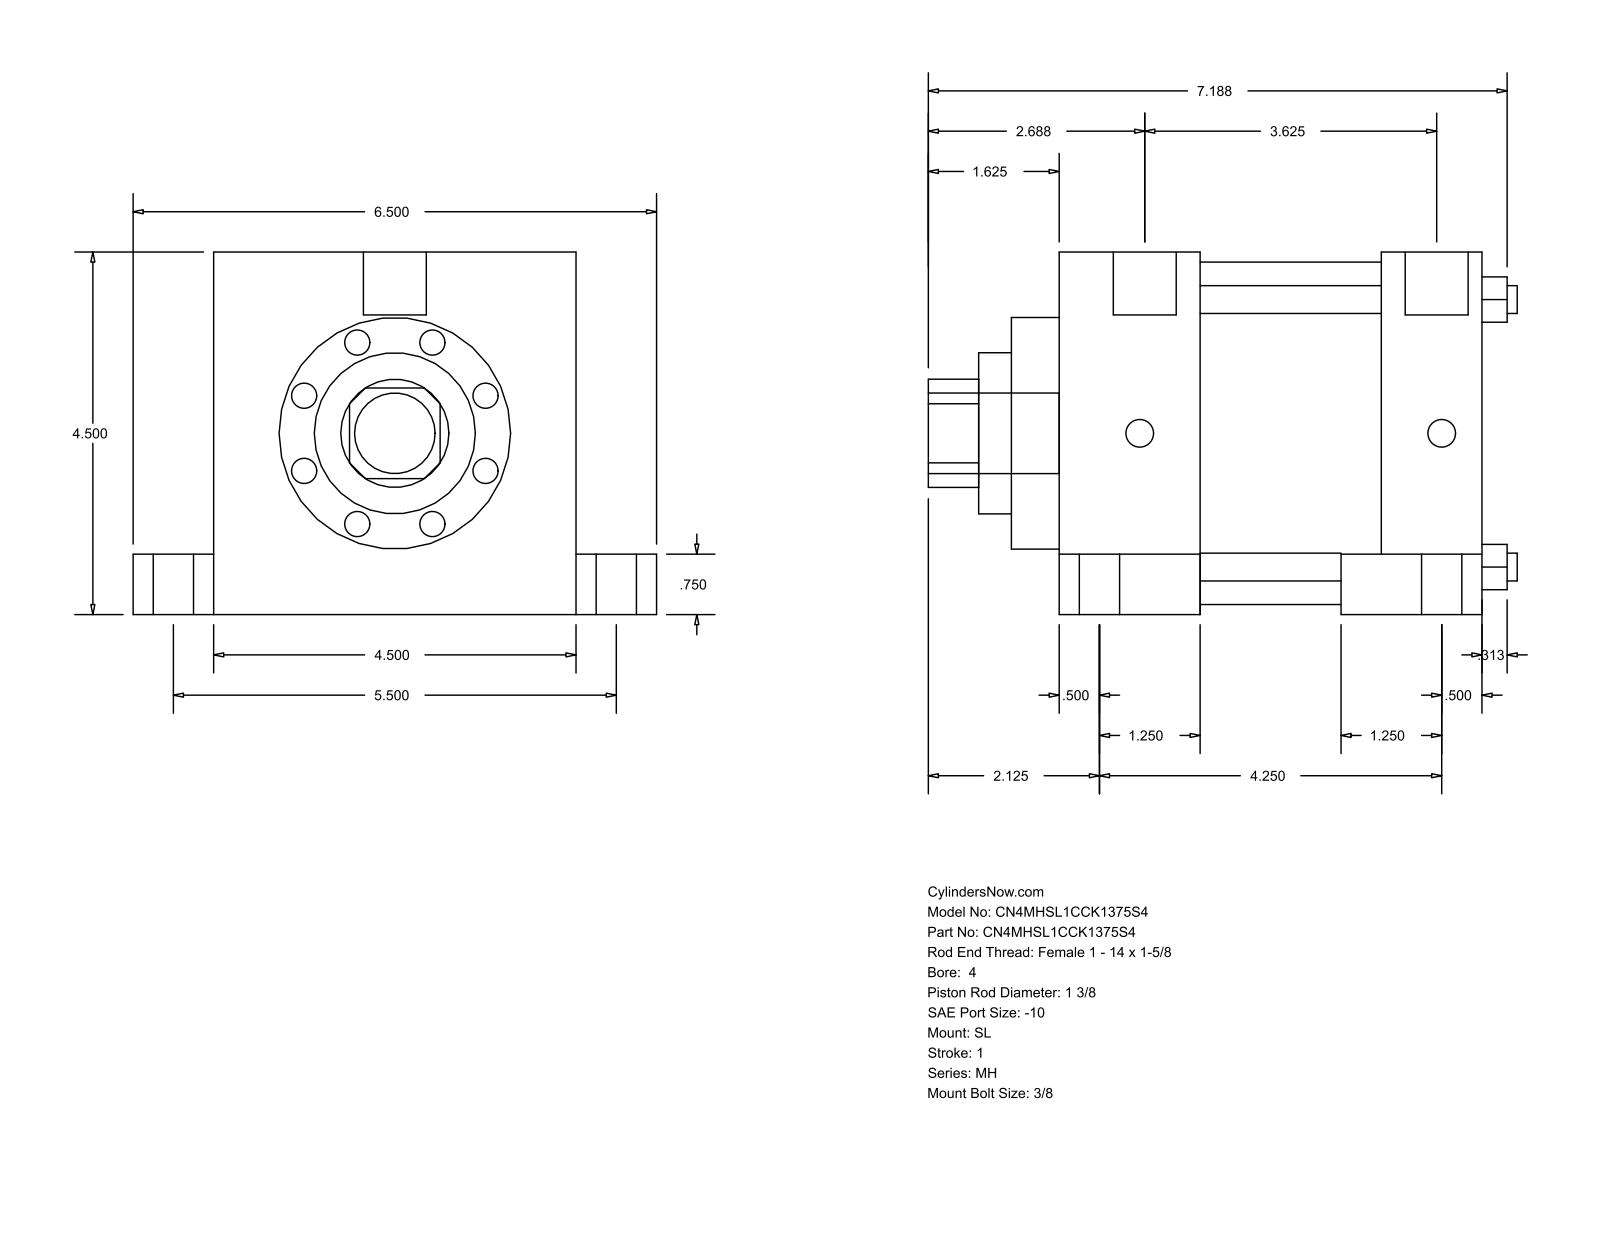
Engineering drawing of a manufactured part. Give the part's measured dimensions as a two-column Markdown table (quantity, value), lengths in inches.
| quantity | value |
| --- | --- |
| part name | MH_SL__0400_1.375 |
| STEP written by | GSSL Pune (CONFIG_CONTROL_DESIGN) |
| units | inches |
| bodies | 0 solids, 110 faces (77 planar, 33 cylindrical, 0 other) |
| overall size | 7.313 × 6.5 × 4.5 |
| round holes (diameter × count) | 0.345 × 4, 1.375 × 1, 2 × 1, 2.875 × 1, 4.25 × 1 |
| round bosses / shafts (diameter × count) | 0.75 × 4, 0.5 × 4, 0.344 × 4, 0.781 × 2, 1 × 1 |
| partial cylindrical surfaces (radius × count) | 0.672 × 1 |
| main face-to-face distances | 4.5, 5.25, 1.75, 3.5, 4, 2.25, 1.25, 1, 5.5, 0.75 |
| hole center spacings | 2.347, 3.32, 4.695 |
